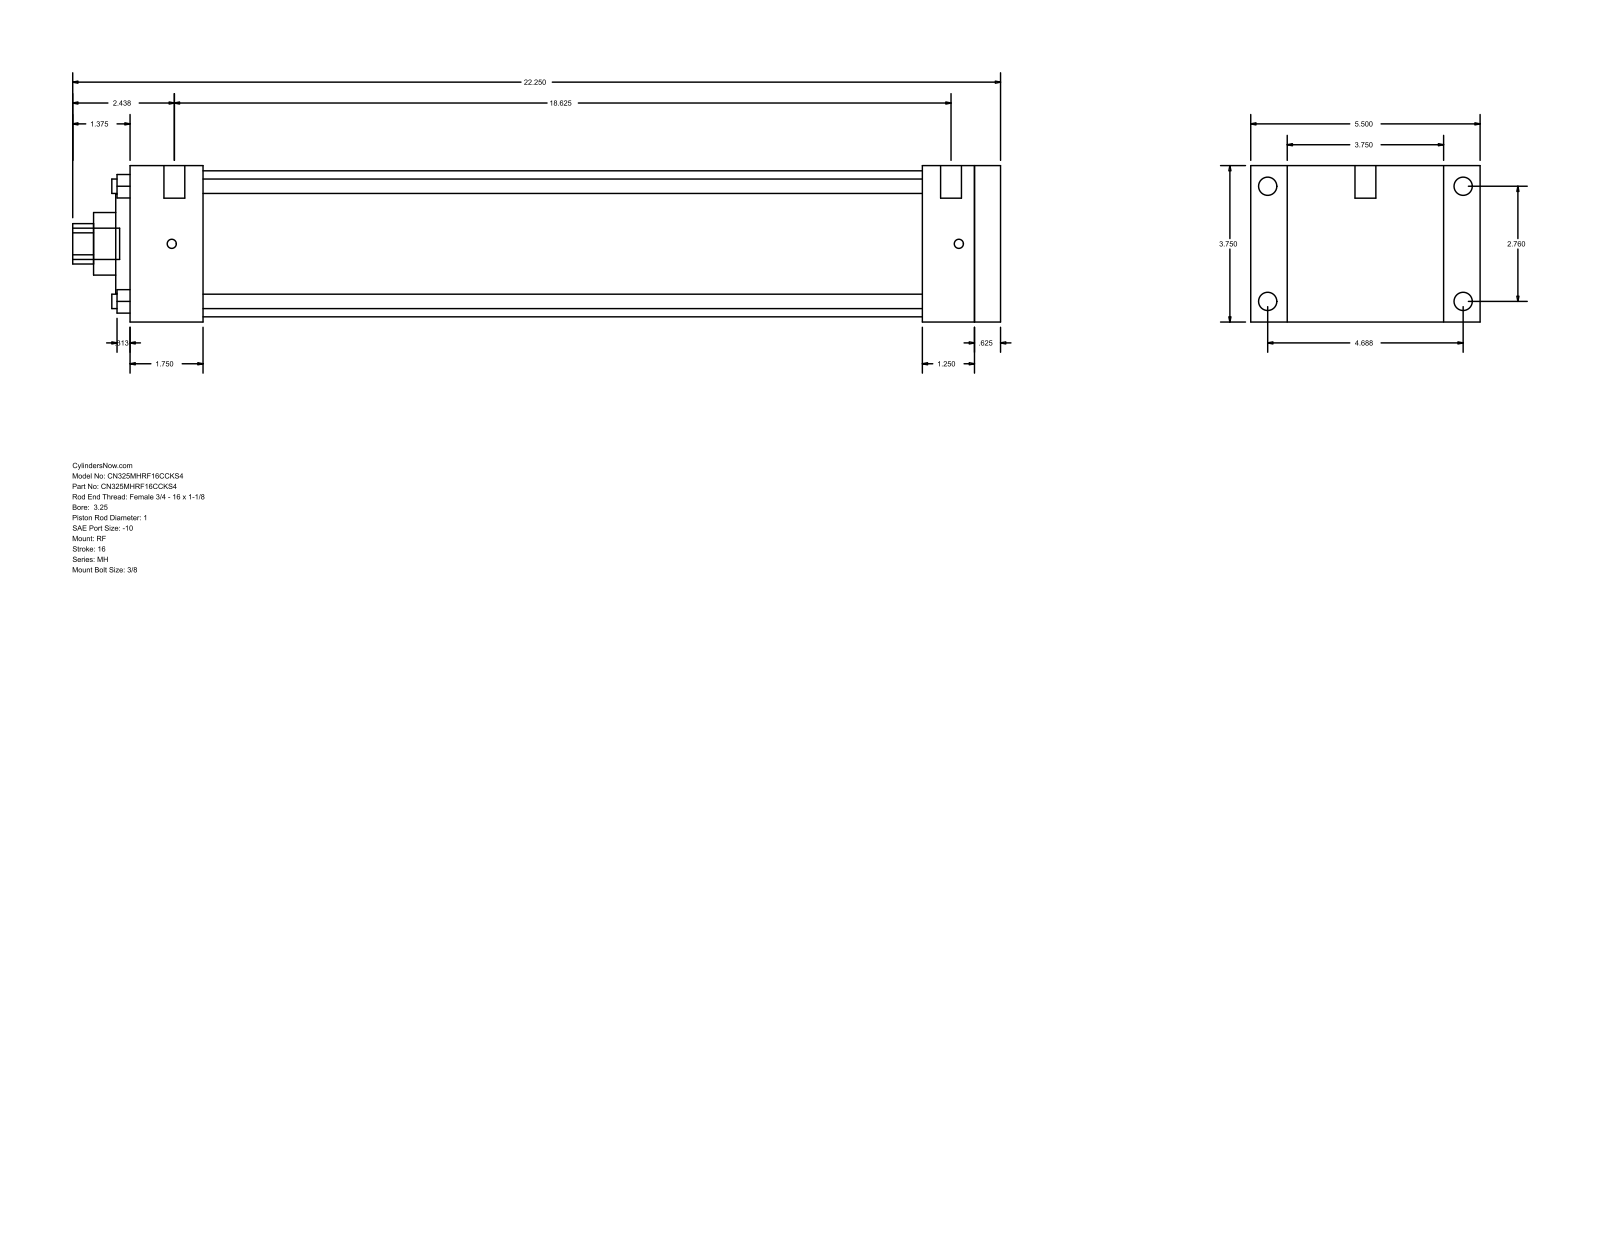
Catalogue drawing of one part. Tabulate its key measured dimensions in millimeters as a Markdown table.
| quantity | value |
| --- | --- |
| part name | MH_RF__0325_1 |
| STEP written by | GSSL Pune (CONFIG_CONTROL_DESIGN) |
| units | millimeters |
| bodies | 0 solids, 94 faces (65 planar, 29 cylindrical, 0 other) |
| overall size | 565.15 × 139.7 × 95.25 |
| round holes (diameter × count) | 8.76 × 4, 25.4 × 1, 38.1 × 1, 60.33 × 1, 88.9 × 1 |
| round bosses / shafts (diameter × count) | 11.13 × 4, 5.56 × 4, 12.7 × 2, 19.05 × 1 |
| partial cylindrical surfaces (radius × count) | 12.29 × 1 |
| main face-to-face distances | 95.24, 530.23, 514.35, 15.88, 22.23, 117.47, 44.46, 469.89, 485.77, 482.6 |
| hole center spacings | 49.57, 70.1, 99.14 |
